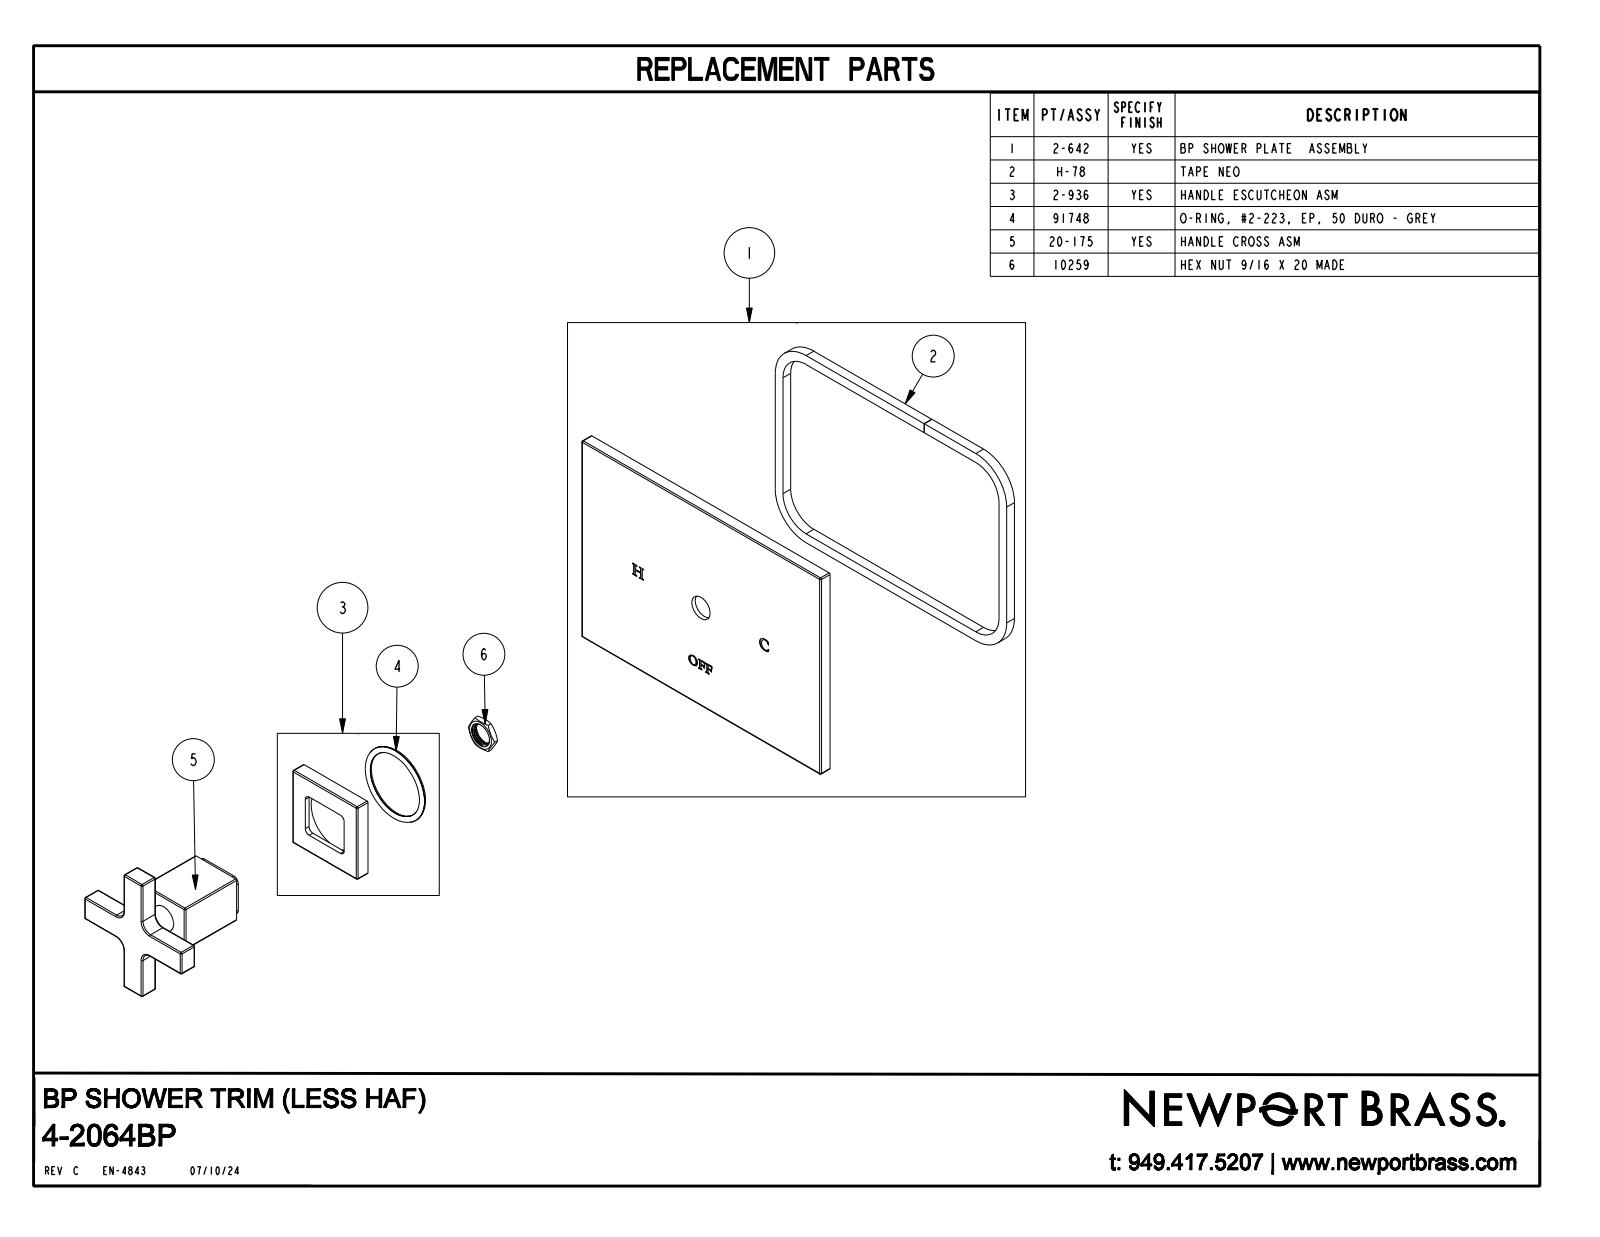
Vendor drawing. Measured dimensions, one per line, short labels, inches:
name: 4-2064BP
written by: CREO PARAMETRIC BY PTC INC, 2018400 (CONFIG_CONTROL_DESIGN)
unit: in
bodies: 1 solid, 351 faces (71 planar, 64 cylindrical, 216 other)
size: 7.75 × 5.5 × 3.356
volume: 19.03 in³; area: 116.9 in²
bosses: 1× ⌀0.65, 1× ⌀0.523
rounds: 48× R0.03, 4× R0.25
face distances: 0.31, 2.17, 3.33, 3.356, 3.046, 3.205, 4.545, 2.906, 2.596, 0.45
